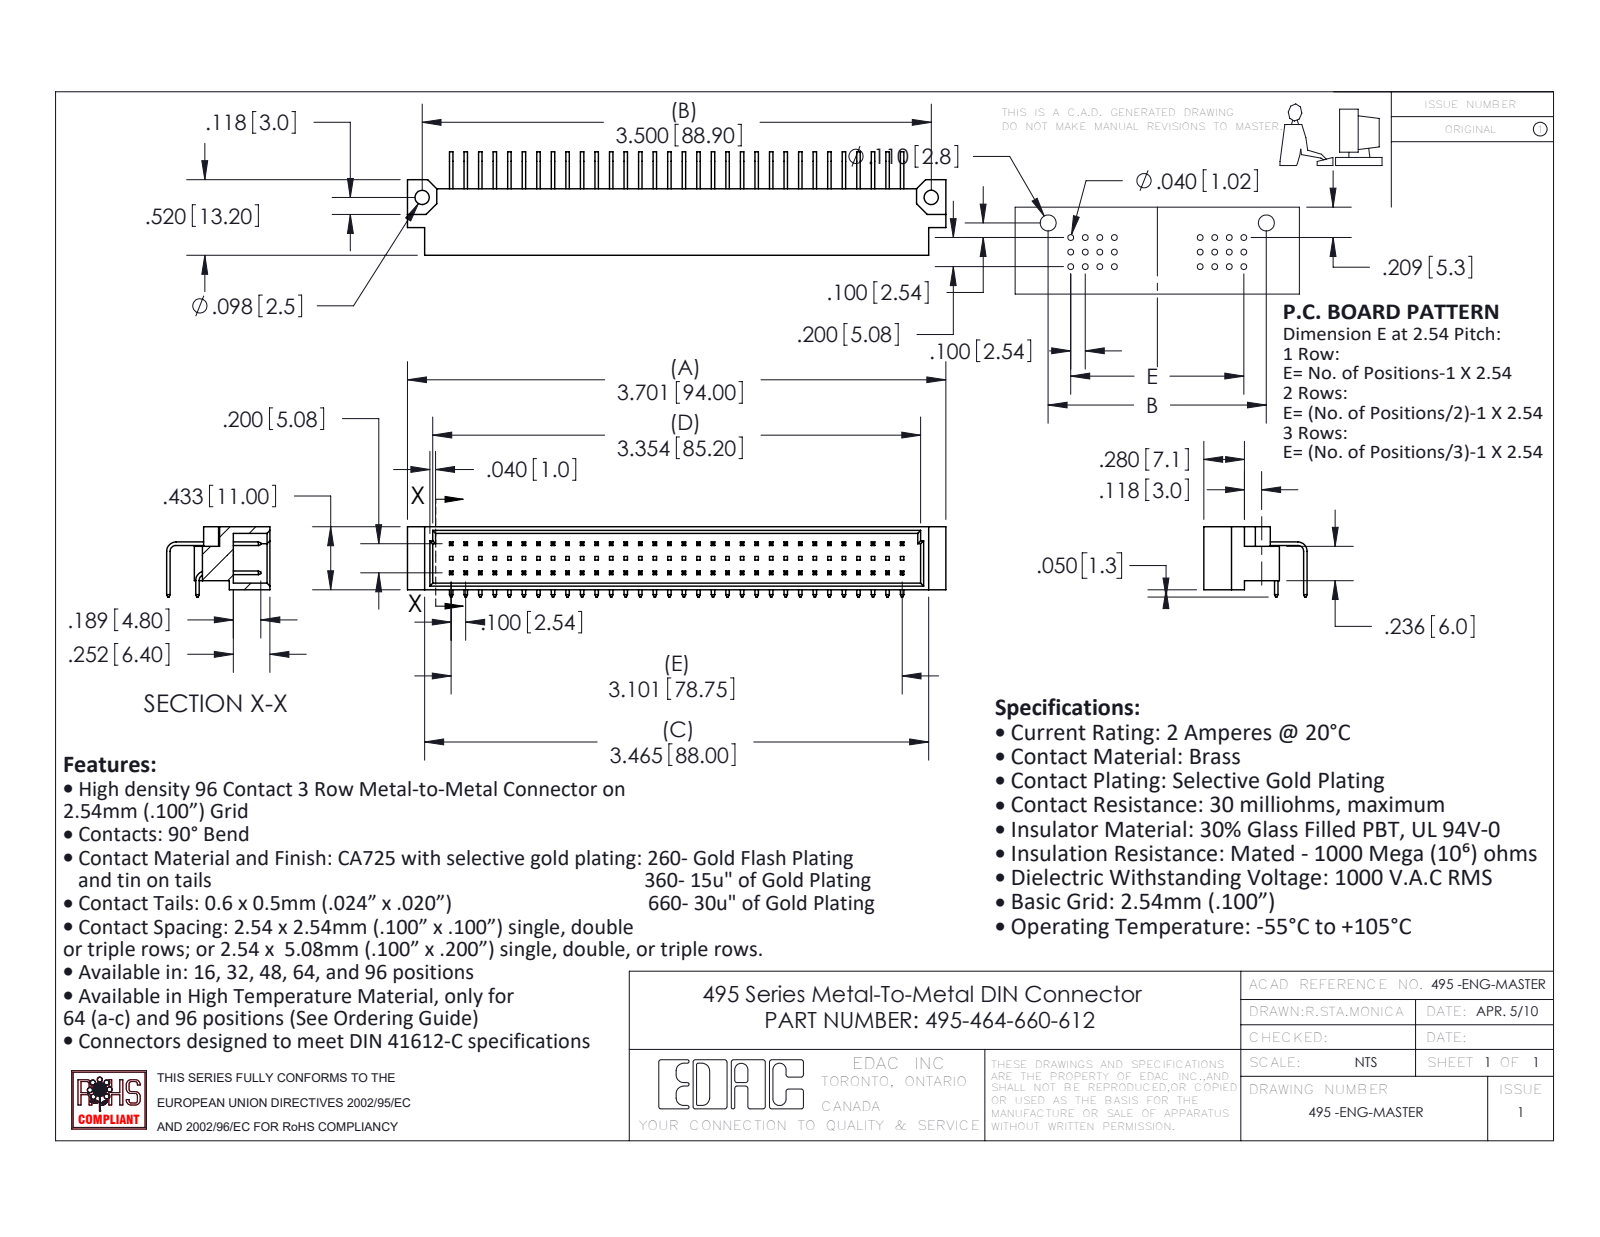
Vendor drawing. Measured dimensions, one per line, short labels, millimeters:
name: 495-290-3; 495 Part_96; 495-464-660-612; 495-290-1
written by: SolidWorks 2020 (AUTOMOTIVE_DESIGN)
unit: mm
bodies: 65 solids, 1585 faces (1453 planar, 132 cylindrical, 0 other)
size: 94 × 18.05 × 12.27
volume: 6 391 mm³; area: 9 910 mm²
holes: 2× ⌀2.49
rounds: 2× R1.02, 2× R1.65
face distances: 1.14, 9.86, 0.61, 5.08, 5.2, 11, 2.54, 8.72, 1.6, 9.4
hole spacings: 88.9
